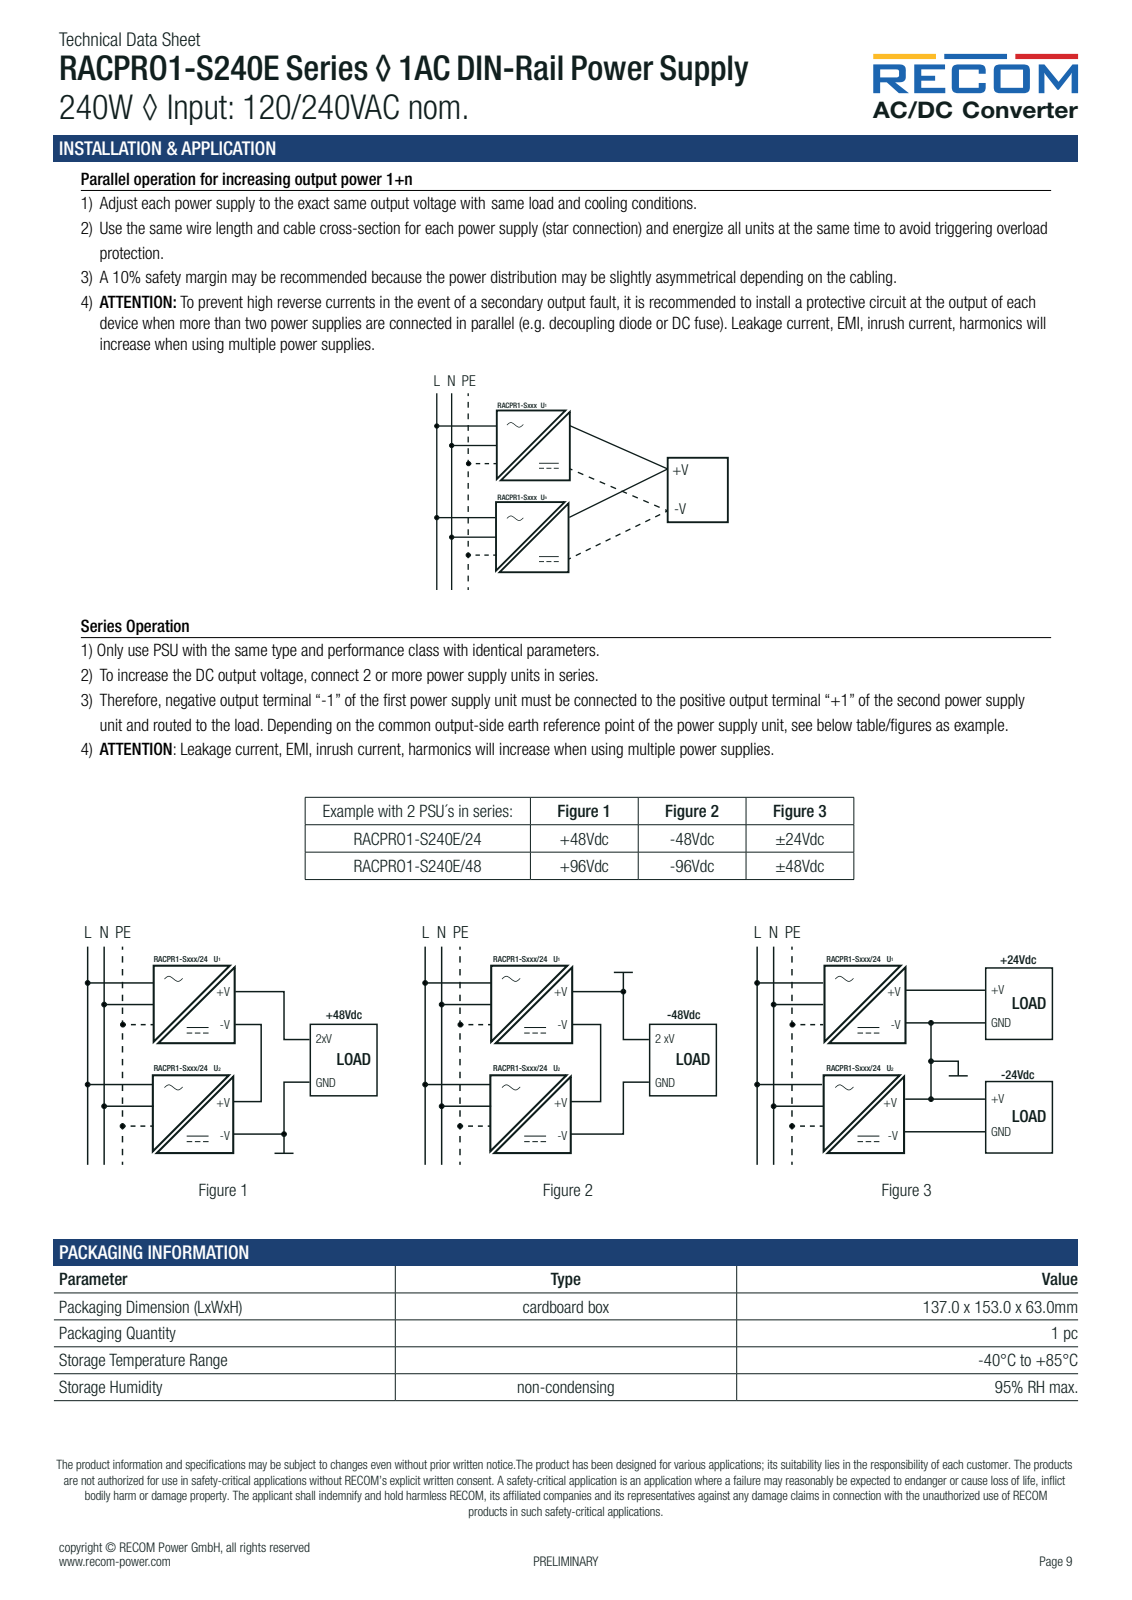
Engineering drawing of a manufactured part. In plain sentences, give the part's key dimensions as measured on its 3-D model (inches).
The part is named "M10xxx-0001_Slider_ND_240W.STEP.STEP; M10773-0001_Isolierfolie_240W.STEP.STEP; TLM-215A-A590-03P(K).stp_2.STEP.STEP; RACPRO_1ph_240W.STEP.STEP (+8 more)". Its 3-D file was written by "SolidWorks 2024 (AUTOMOTIVE_DESIGN)". It is 12 solids with 3248 faces: 2081 planar, 885 cylindrical and 282 other. Overall it measures 5.76 by 4.921 by 1.535 inches. Its volume is 6.894 cubic inches and its surface area 313.9 square inches. Round holes: 28 of diameter 0.047, 14 of diameter 0.083, 12 of diameter 0.039, 11 of diameter 0.051, 10 of diameter 0.035, 8 of diameter 0.063, 6 of diameter 0.059, 5 of diameter 0.043, 5 of diameter 0.094, 4 of diameter 0.02, 4 of diameter 0.055, 4 of diameter 0.079. Round bosses or shafts: 1 of diameter 0.197, 1 of diameter 0.157, 1 of diameter 0.118. Partial cylindrical surfaces (rounded edges, fillets, slot ends): 75 of radius 0.012, 38 of radius 0.02, 29 of radius 0.039, 24 of radius 0.006, 22 of radius 0.004, 20 of radius 0.008, 18 of radius 0.031, 10 of radius 0.006. The main face-to-face distances are 0.049, 0.061, 1.474, 1.486, 1.425, 0.039, 0.022, 1.496, 1.435, 1.447. The hole center spacings are 0.197, 0.394, 0.378, 0.213, 0.249, 0.323, 0.509, 0.591.
